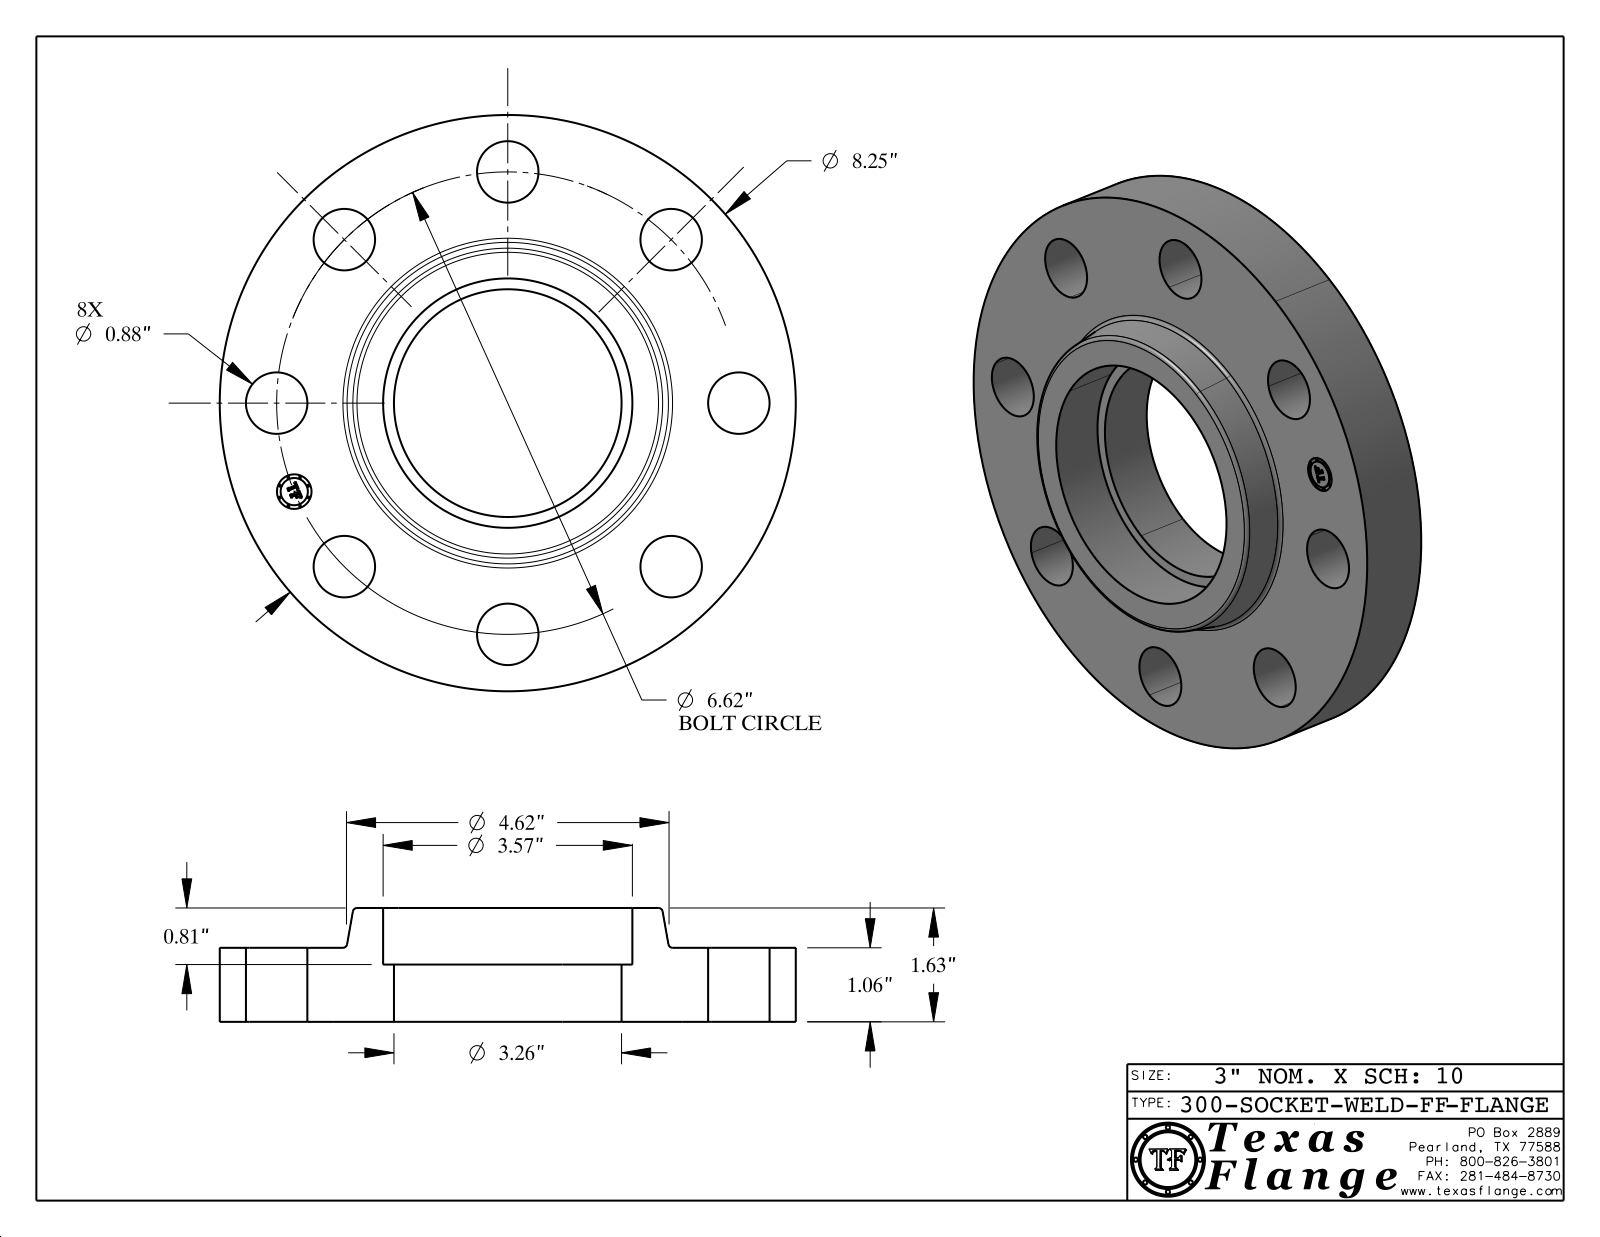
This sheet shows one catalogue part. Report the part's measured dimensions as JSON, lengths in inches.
{"part_name": "300-SOCKET-WELD-FF", "step_written_by": "CATIA V5 STEP AP214 (AUTOMOTIVE_DESIGN)", "units": "inches", "bodies": {"solids": 1, "faces": 418, "planar": 370, "cylindrical": 42, "other": 6}, "overall_size": [8.25, 8.25, 1.63], "volume_in3": 45.7, "surface_area_in2": 155.3, "round_holes": [[0.88, 8], [0.495, 1], [3.26, 1], [3.57, 1]], "round_bosses_or_shafts": [[0.03, 8], [8.25, 1], [0.39, 1]], "face_to_face_distances": [1.06, 1.63, 0.57, 0.82, 0.24, 0.81, 0.015, 1.045, 0.225, 0.585], "hole_center_spacings": [3.31, 2.533, 6.116, 4.681, 4.681, 1.291, 3.678, 6.493]}
